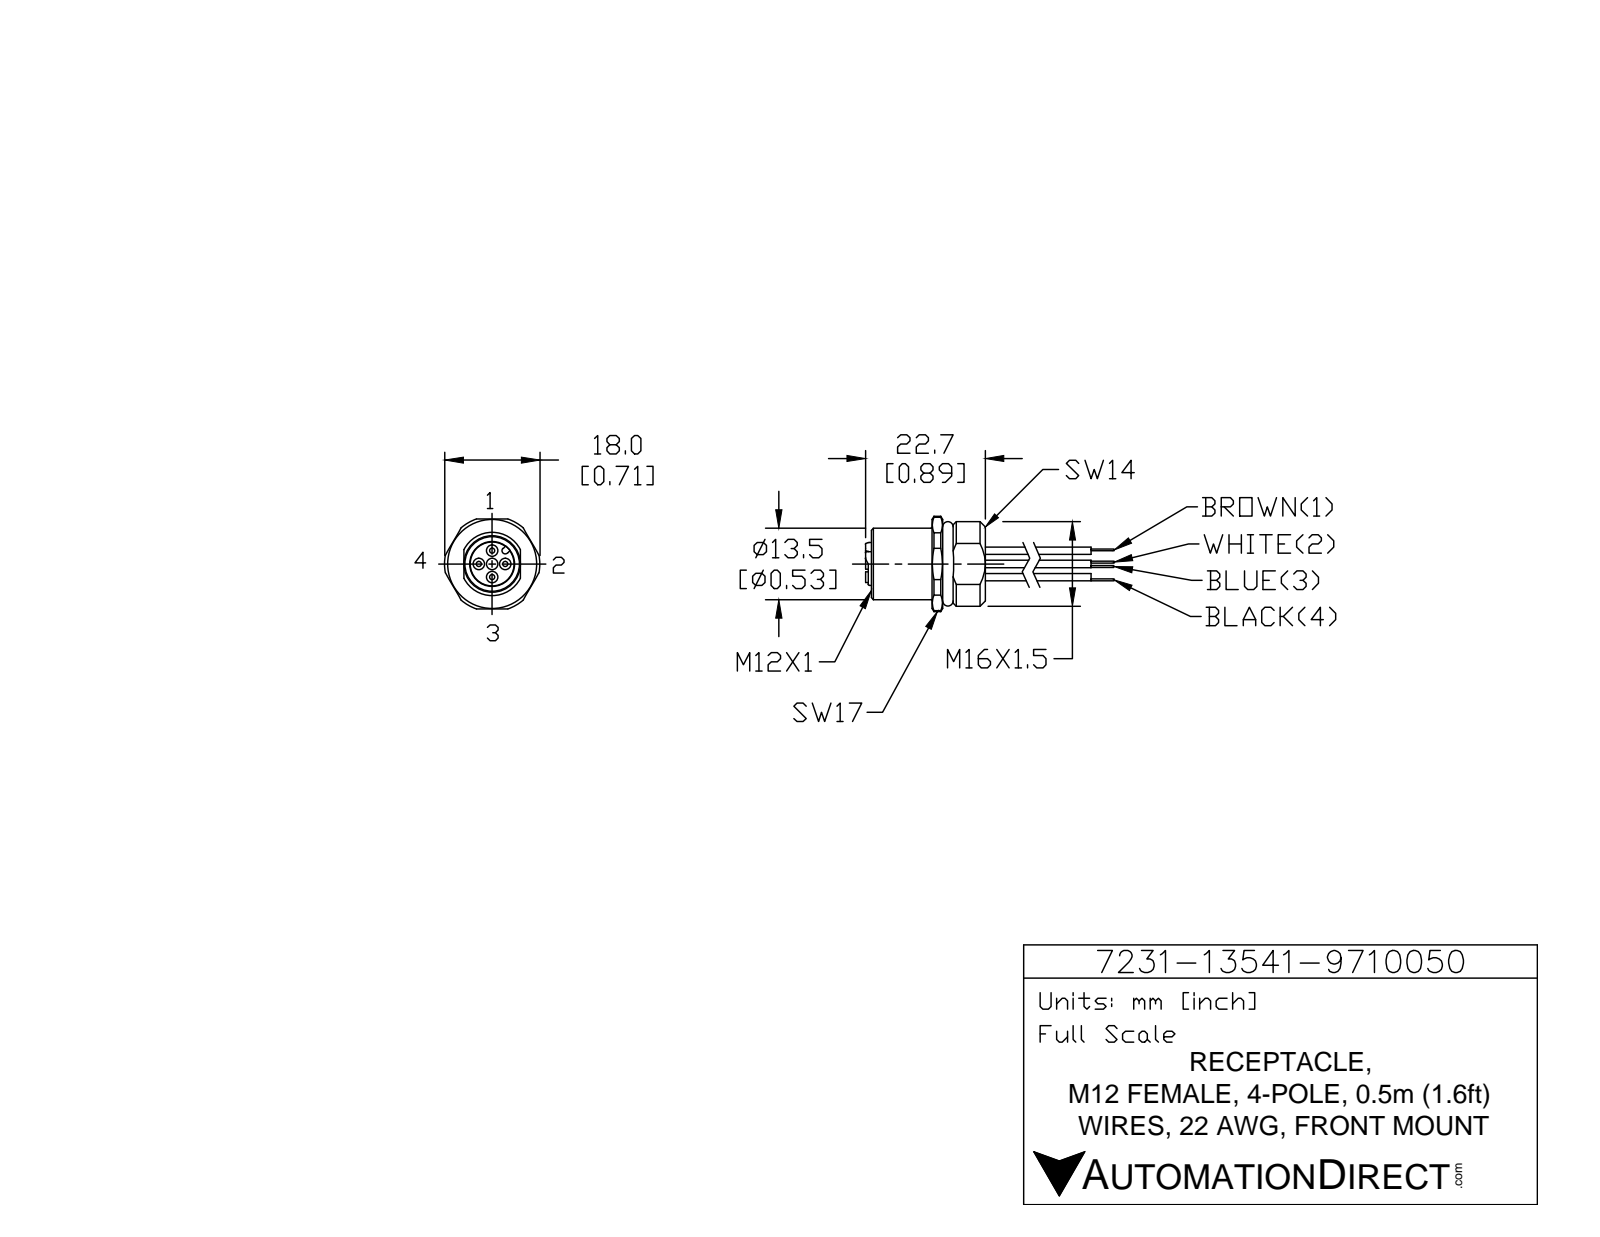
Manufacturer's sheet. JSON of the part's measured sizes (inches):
{"part_name": "7231-13541-9710050", "step_written_by": "SolidWorks 2018 (AUTOMOTIVE_DESIGN)", "units": "inches", "bodies": {"solids": 1, "faces": 153, "planar": 38, "cylindrical": 63, "other": 52}, "overall_size": [1.677, 0.709, 0.669], "volume_in3": 0.204, "surface_area_in2": 3.825, "round_holes": [[0.043, 5], [0.43, 1], [0.48, 1], [0.512, 1]], "round_bosses_or_shafts": [[0.079, 5], [0.055, 4], [0.531, 1], [0.319, 1]], "partial_cylinders_radius": [[0.008, 6], [0.024, 1], [0.315, 1], [0.354, 1]], "face_to_face_distances": [0.276, 0.555, 0.354, 0.079, 0.28, 0.201, 0.551, 0.831, 0.039, 0.669], "hole_center_spacings": [0.098, 0.139, 0.197, 0.098, 0.099]}
